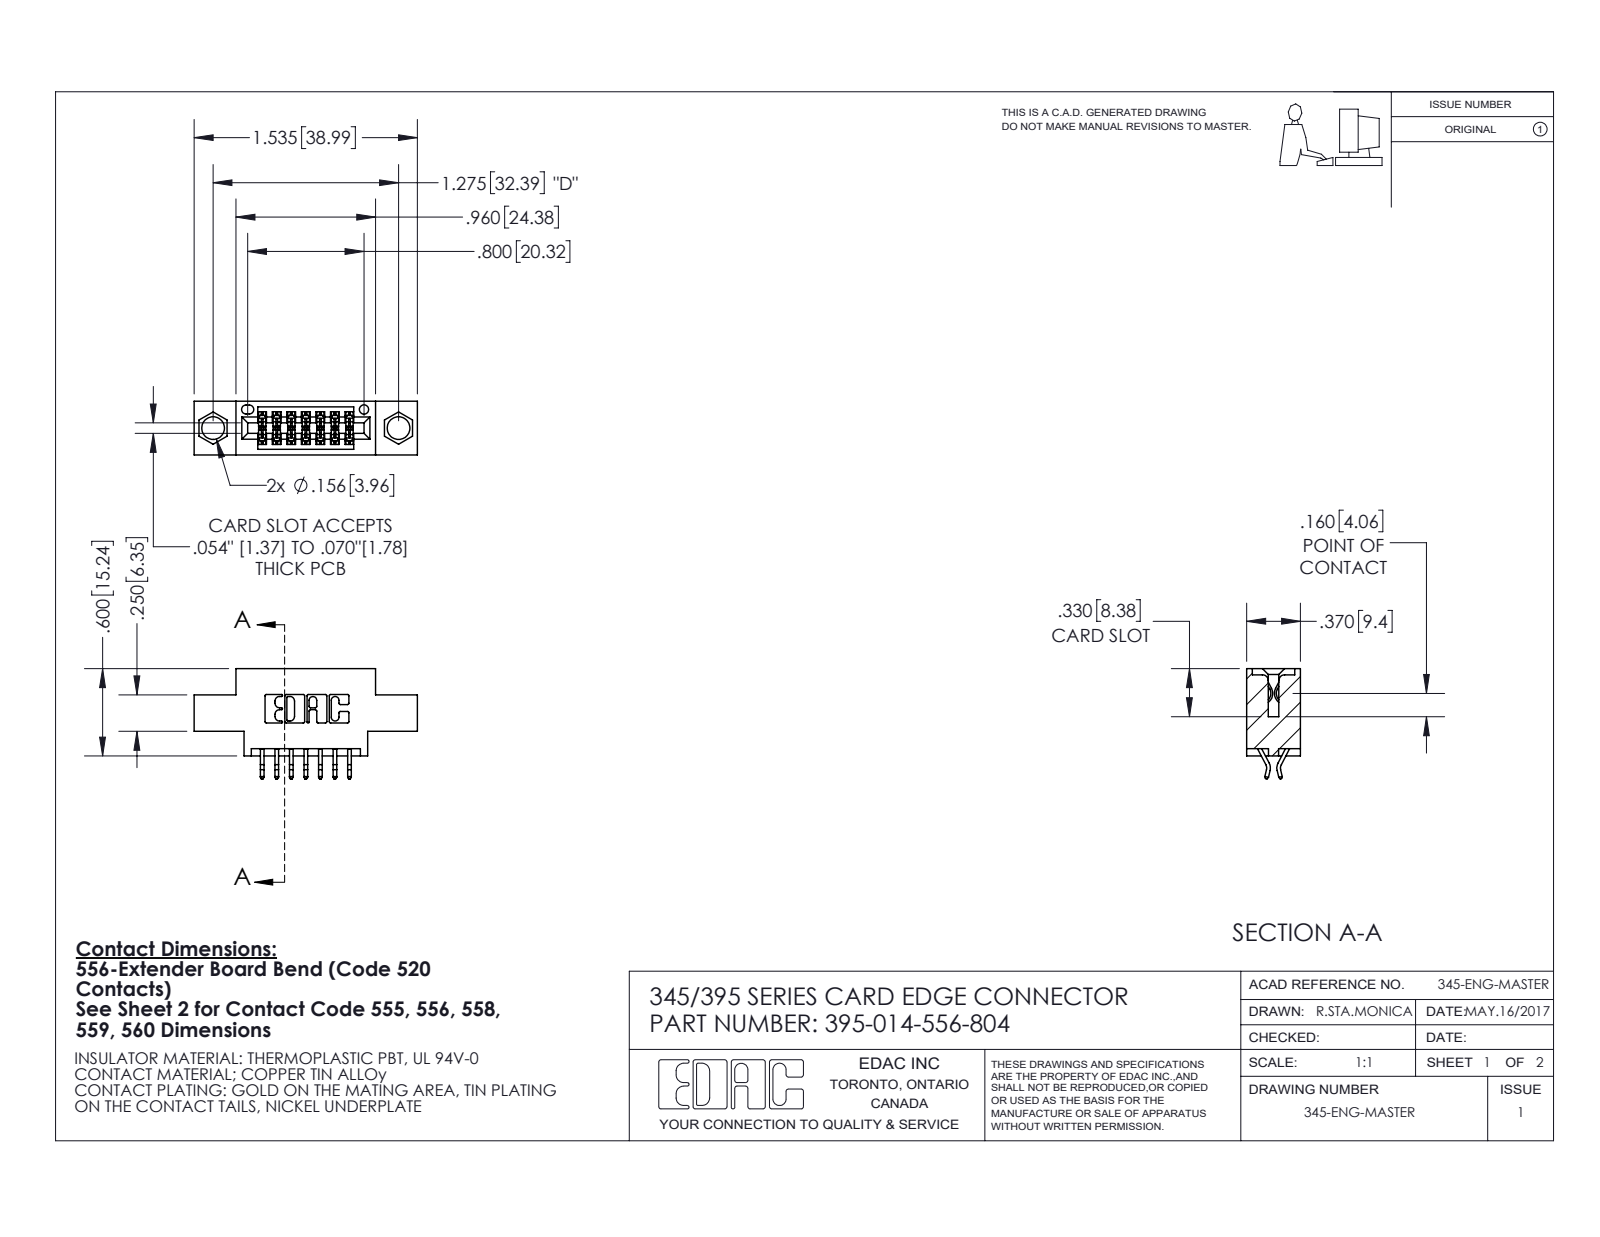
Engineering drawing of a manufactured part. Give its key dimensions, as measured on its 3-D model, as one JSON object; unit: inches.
{"part_name": "345-292-001_556 Tail; 395-014-556-804; 345 Part_0.170 Offset - 0.156 Dia-TI", "step_written_by": "SolidWorks 2020 (CONFIG_CONTROL_DESIGN)", "units": "inches", "bodies": {"solids": 15, "faces": 928, "planar": 616, "cylindrical": 312, "other": 0}, "overall_size": [1.535, 0.757, 0.37], "volume_in3": 0.198, "surface_area_in2": 6.352, "round_holes": [[0.156, 2], [0.064, 1]], "partial_cylinders_radius": [[0.006, 28], [0.01, 22], [0.007, 6], [0.031, 6], [0.026, 3], [0.01, 2], [0.014, 2], [0.019, 2]], "face_to_face_distances": [0.2, 0.37, 0.1, 0.072, 0.298, 0.3, 0.025, 0.098, 0.272, 0.06], "hole_center_spacings": [0.27, 1.045, 1.275]}
